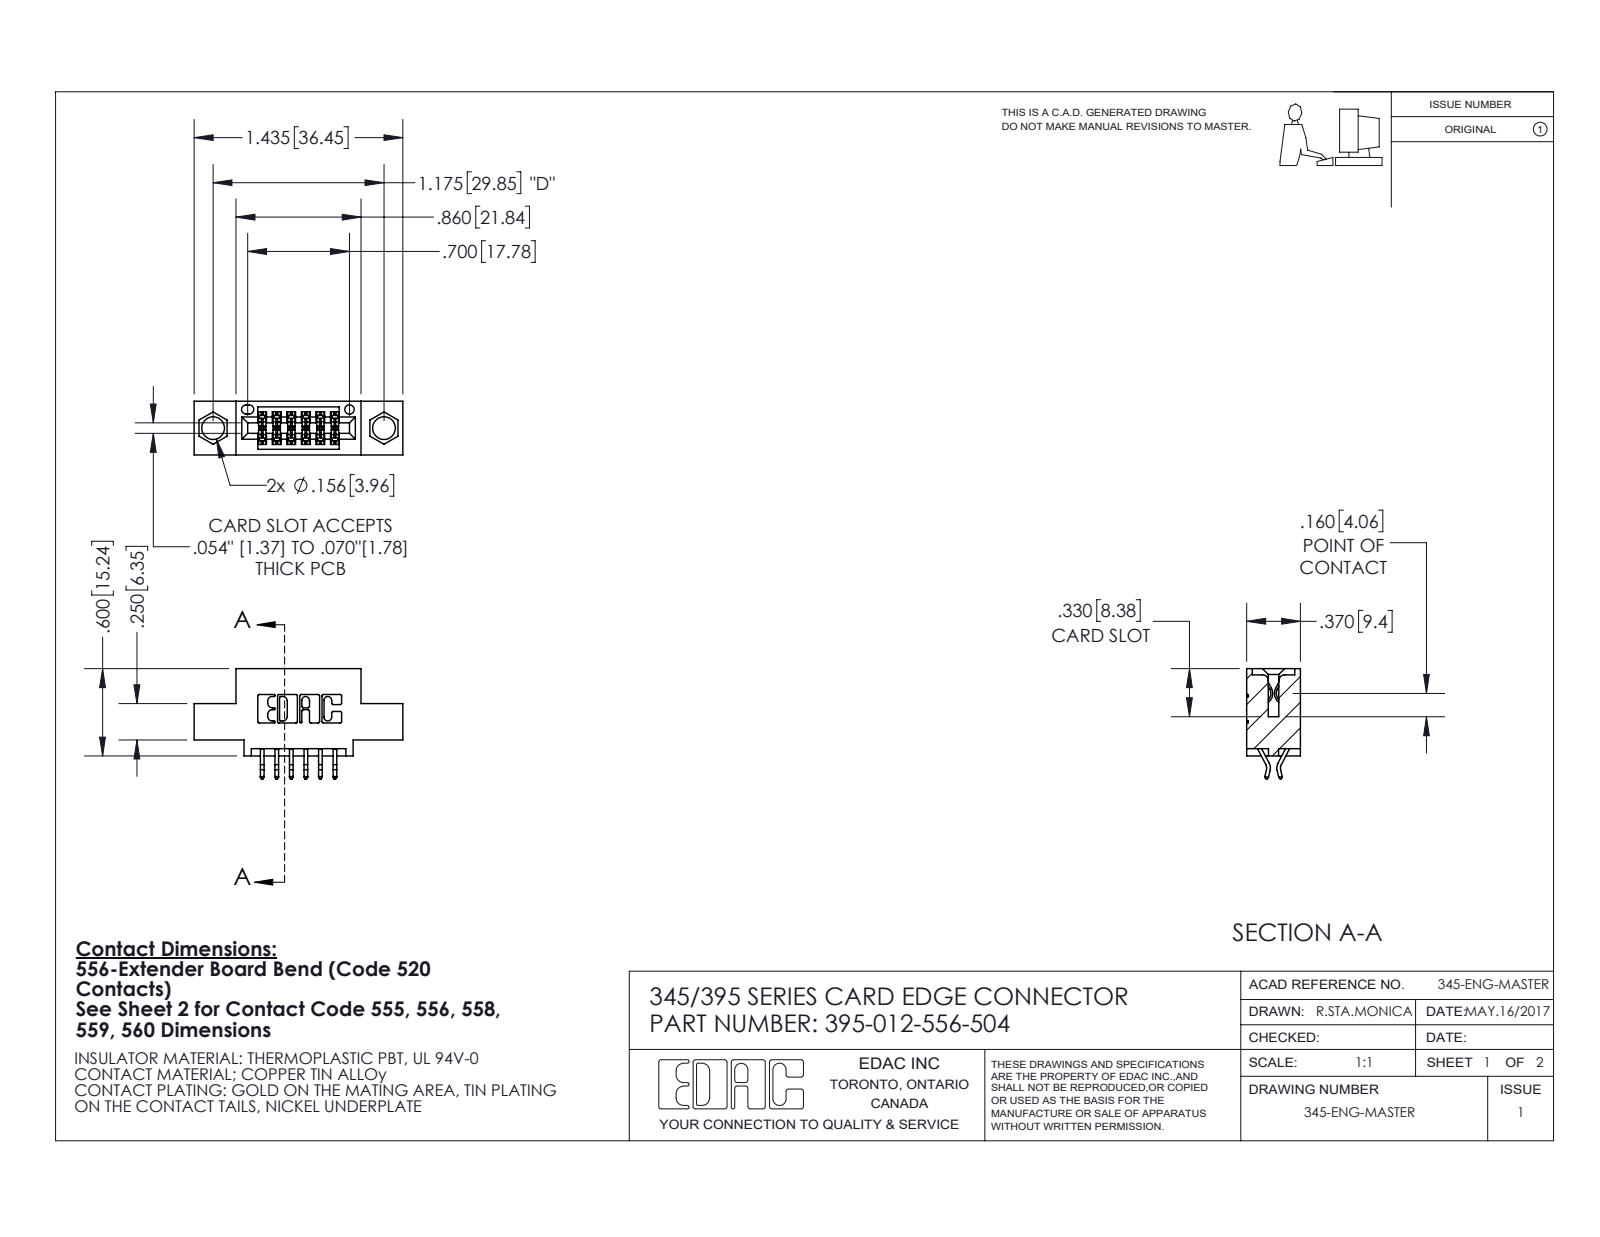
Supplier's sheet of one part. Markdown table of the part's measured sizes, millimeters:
| quantity | value |
| --- | --- |
| part name | 345-292-001_556 Tail; 395-012-556-504; 345 Part_0.110 Offset - 0.156 Dia-TI |
| STEP written by | SolidWorks 2020 (CONFIG_CONTROL_DESIGN) |
| units | millimeters |
| bodies | 13 solids, 816 faces (542 planar, 274 cylindrical, 0 other) |
| overall size | 36.4 × 19.2 × 9.4 |
| volume | 3 030 mm³ |
| surface area | 3 711 mm² |
| round holes (diameter × count) | 4 × 2, 1.6 × 1 |
| partial cylindrical surfaces (radius × count) | 0.2 × 24, 0.3 × 22, 0.2 × 6, 0.8 × 6, 0.7 × 3, 0.3 × 2, 0.4 × 2, 0.5 × 2 |
| main face-to-face distances | 5.1, 9.4, 7.6, 1.8, 2.5, 0.6, 2.5, 6.9, 4.1, 1.5 |
| hole center spacings | 6.9, 24, 29.8 |
